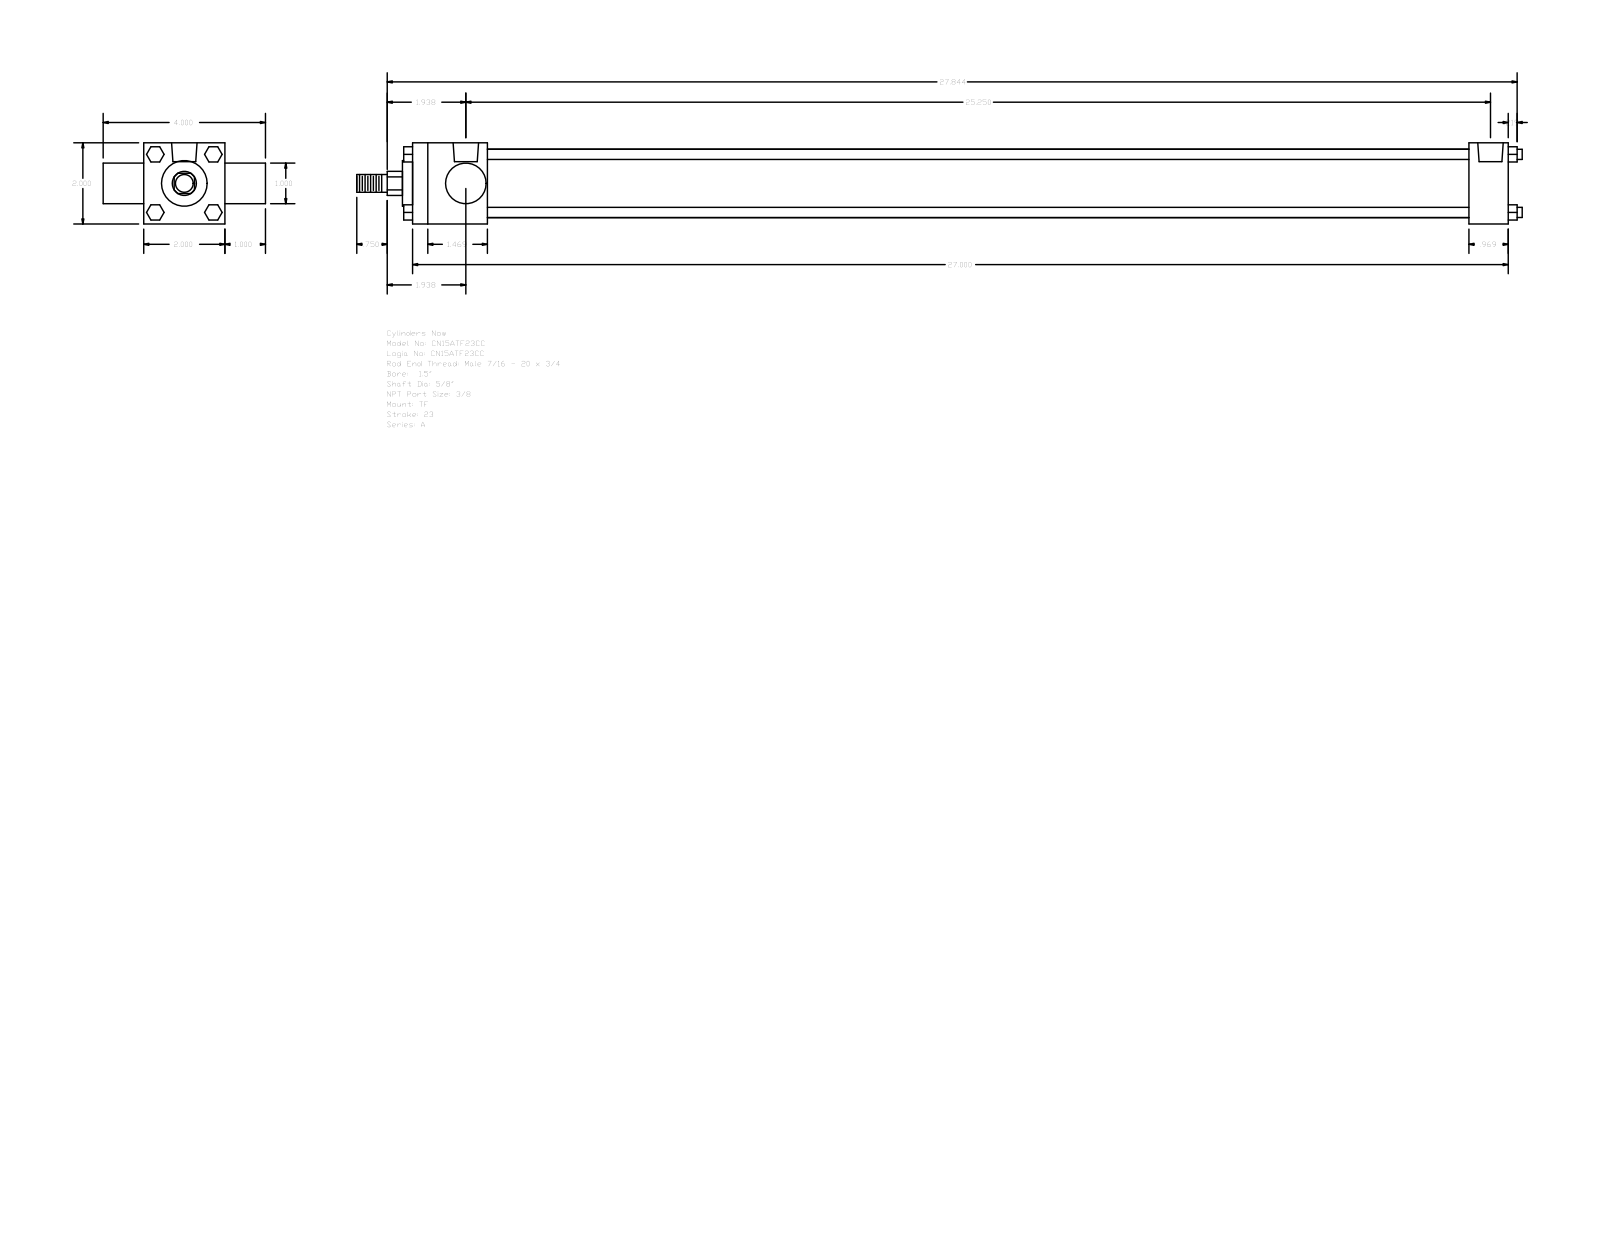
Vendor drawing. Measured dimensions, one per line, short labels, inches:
name: A_TF__0150_0.625
written by: GSSL Pune (CONFIG_CONTROL_DESIGN)
unit: in
bodies: 0 solids, 120 faces (92 planar, 28 cylindrical, 0 other)
size: 28.719 × 4 × 2
holes: 3× ⌀0.219, 2× ⌀0.627
bosses: 4× ⌀0.25, 1× ⌀1.69, 1× ⌀1.125, 1× ⌀1, 1× ⌀0.625, 1× ⌀0.437
rounds: 1× R0.297
face distances: 2, 27, 1, 3, 1.844, 26.031, 24.187, 25.156, 0.969, 4
hole spacings: 0.156, 25.094, 24.937, 25.25
